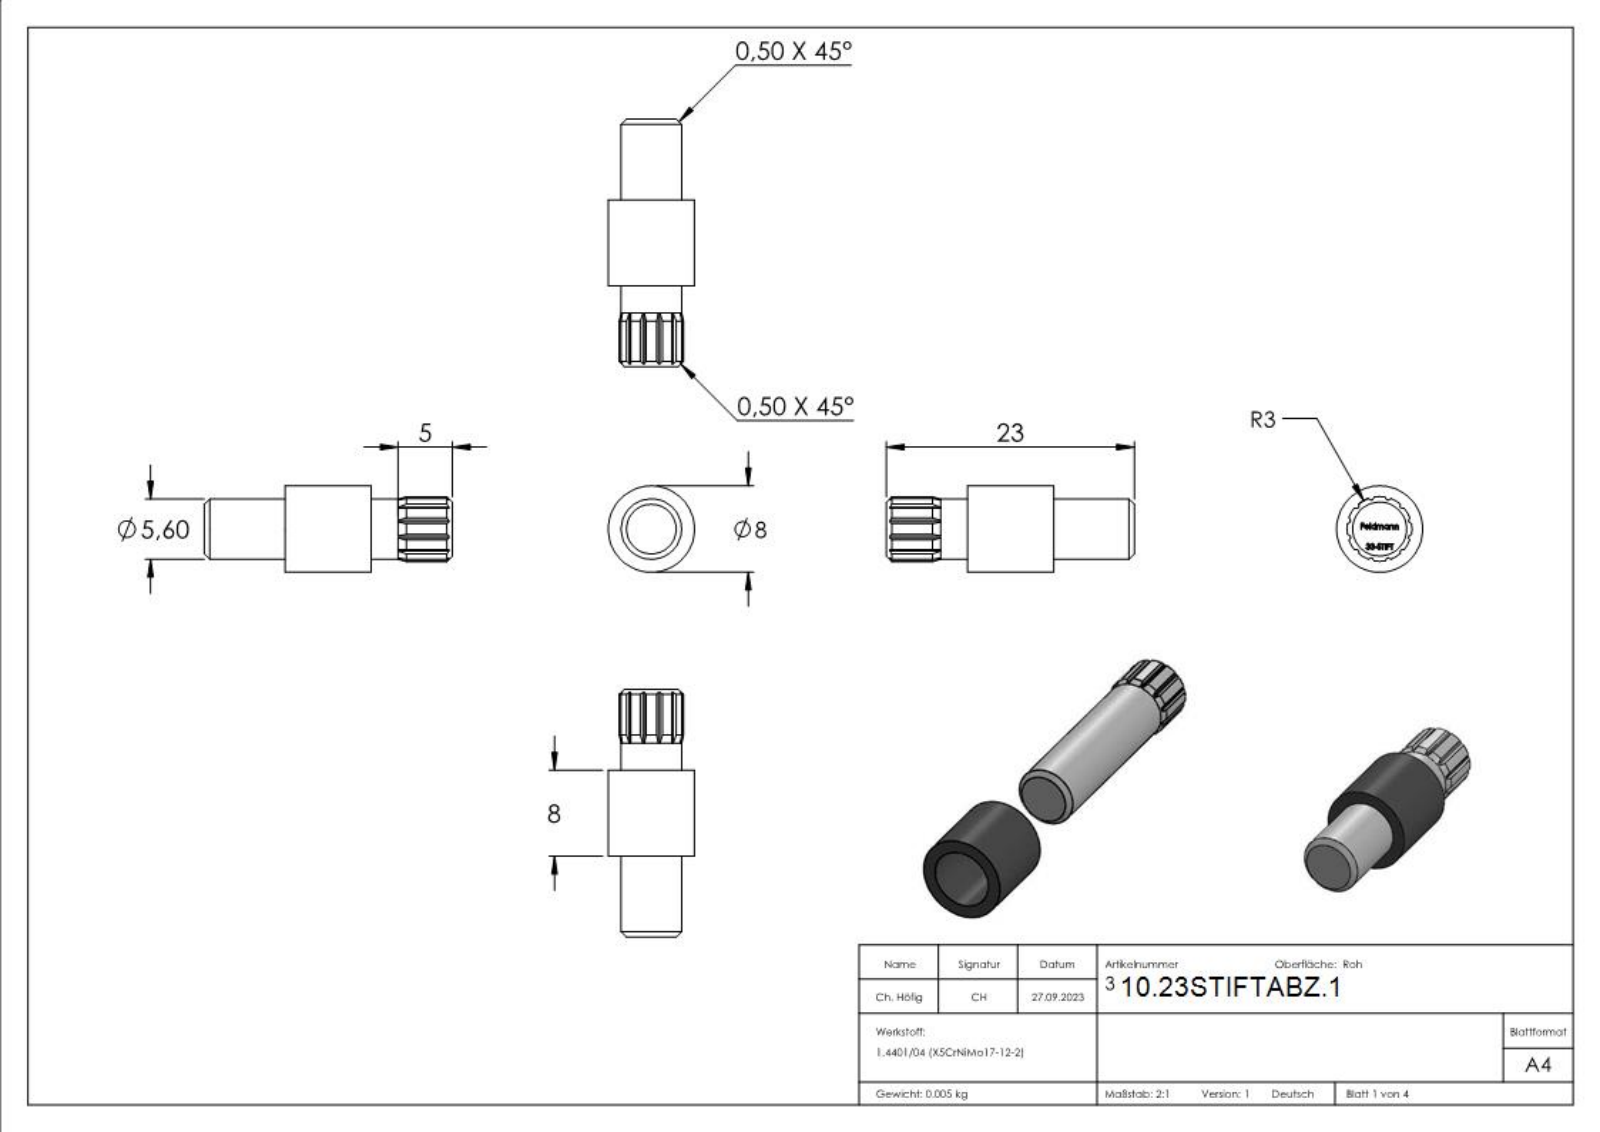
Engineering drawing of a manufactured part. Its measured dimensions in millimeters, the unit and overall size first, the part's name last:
Units: millimetres
Overall size (bounding box): 23 × 8 × 8
Round holes (diameter × count): ⌀5.6 ×1
Round bosses / shafts (diameter × count): ⌀8 ×1
Partial cylindrical surfaces — rounded edges, fillets, slot ends (radius × count): R3 ×1
Main face-to-face distances: 7.5, 15.5, 8, 23, 4.04, 4.02, 7.4, 15.4, 22.9, 1.35
Volume: 780 mm³ · Surface area: 856 mm²
Bodies: 2 solids, 263 faces (143 planar, 15 cylindrical, 105 other)
Part name (STEP PRODUCT): 33-STIFT; 33-STIFT Teil2_33-STIFT Teil2; 33-STIFT Teil1_33-STIFT Teil1
STEP written by: SolidWorks 2018 (CONFIG_CONTROL_DESIGN)
